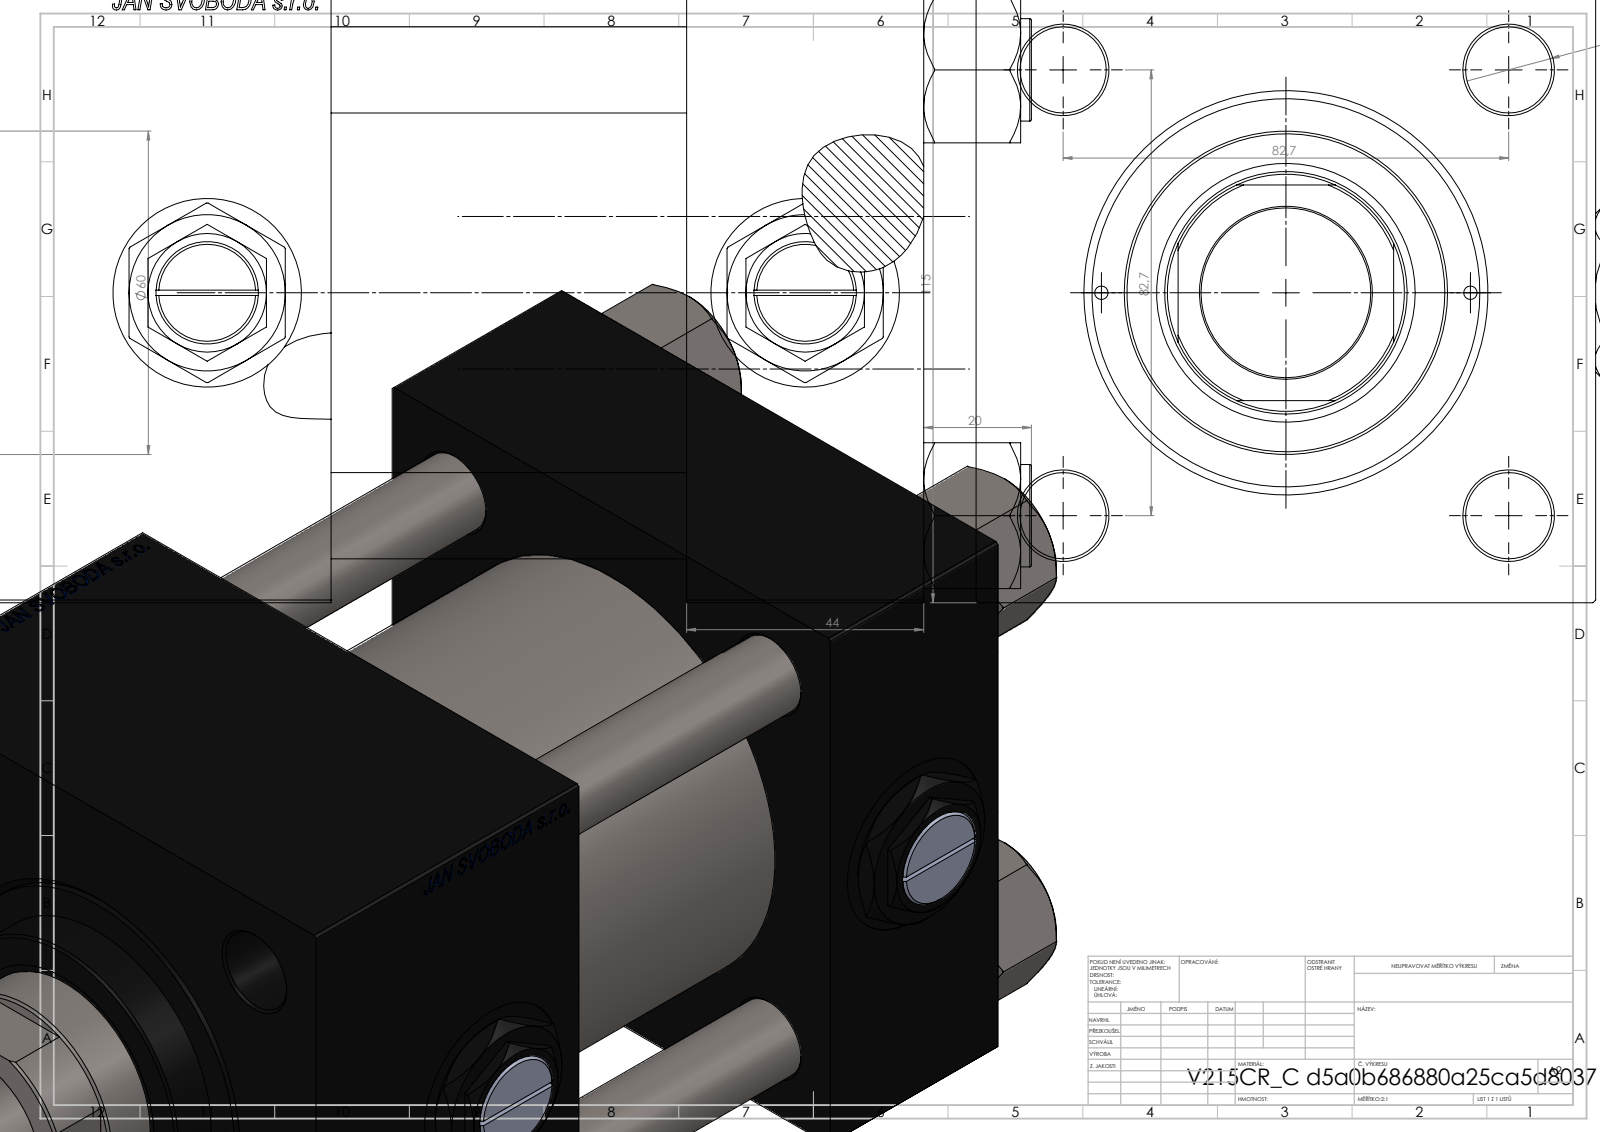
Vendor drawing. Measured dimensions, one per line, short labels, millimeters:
name: V215CR_C_TYCINKA; NUT_M5_C; V215_VC_A; Zatka_pro_OIL_PORT (+2 more)
written by: SolidWorks 2019 (CONFIG_CONTROL_DESIGN)
unit: mm
bodies: 13 solids, 1303 faces (623 planar, 102 cylindrical, 578 other)
size: 230 × 122 × 115
volume: 1 805 000 mm³; area: 280 871 mm²
holes: 4× ⌀16, 2× ⌀2.5, 2× ⌀7, 2× ⌀26.44, 2× ⌀35, 1× ⌀31.5, 1× ⌀45, 1× ⌀48, 1× ⌀61, 1× ⌀72, 1× ⌀80
bosses: 4× ⌀19, 1× ⌀86, 1× ⌀60
rounds: 1× R22
face distances: 115, 44, 110, 179, 135, 69, 66, 20, 150.3, 106.3
hole spacings: 41.96, 58.48, 82.7, 86.17, 34.25, 116.96, 68.5, 111
